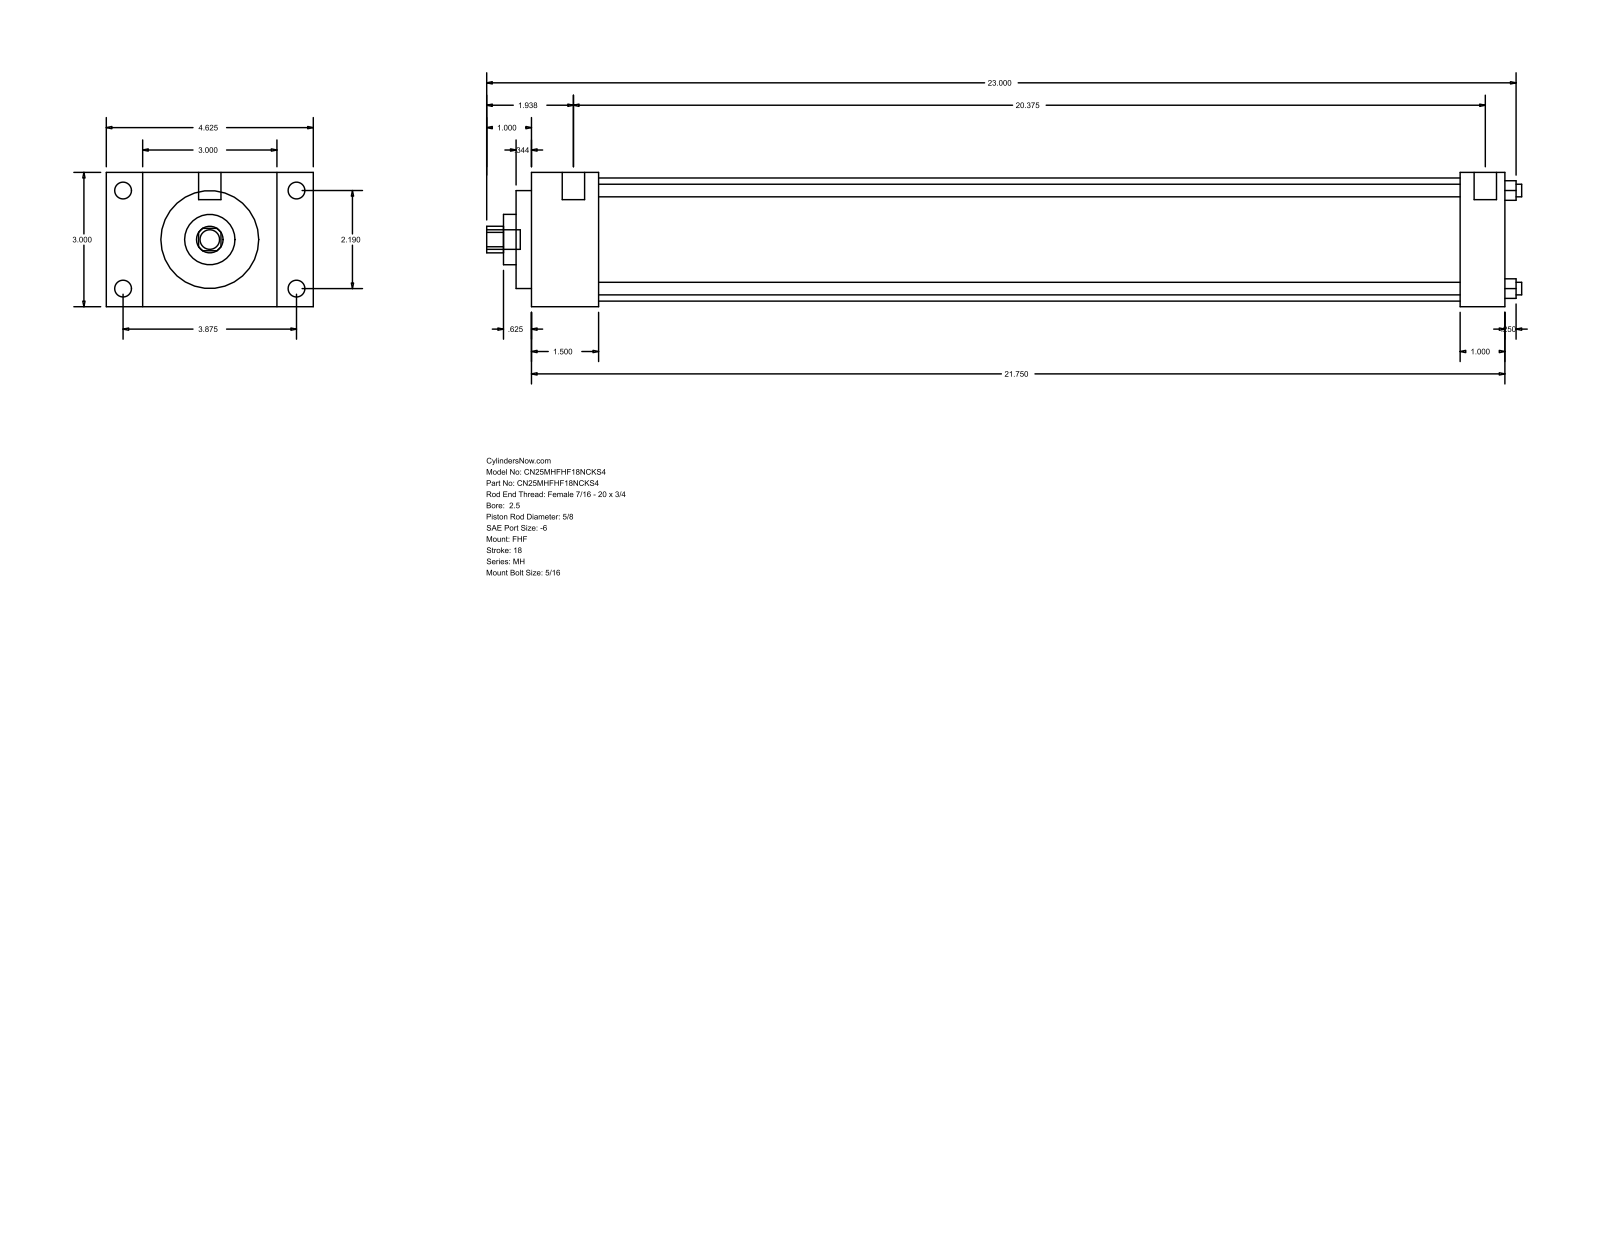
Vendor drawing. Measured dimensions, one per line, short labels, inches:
name: MH_FHF__0250_0.625
written by: GSSL Pune (CONFIG_CONTROL_DESIGN)
unit: in
bodies: 0 solids, 90 faces (61 planar, 29 cylindrical, 0 other)
size: 23.125 × 4.625 × 3
holes: 4× ⌀0.281, 1× ⌀0.625, 1× ⌀1.125, 1× ⌀2.187, 1× ⌀2.75
bosses: 4× ⌀0.375, 4× ⌀0.219, 2× ⌀0.5, 1× ⌀0.437
rounds: 1× R0.297
face distances: 3, 21.75, 1.5, 20.25, 0.813, 3.813, 4.625, 1, 20.75, 19.25
hole spacings: 1.548, 2.19, 3.097
